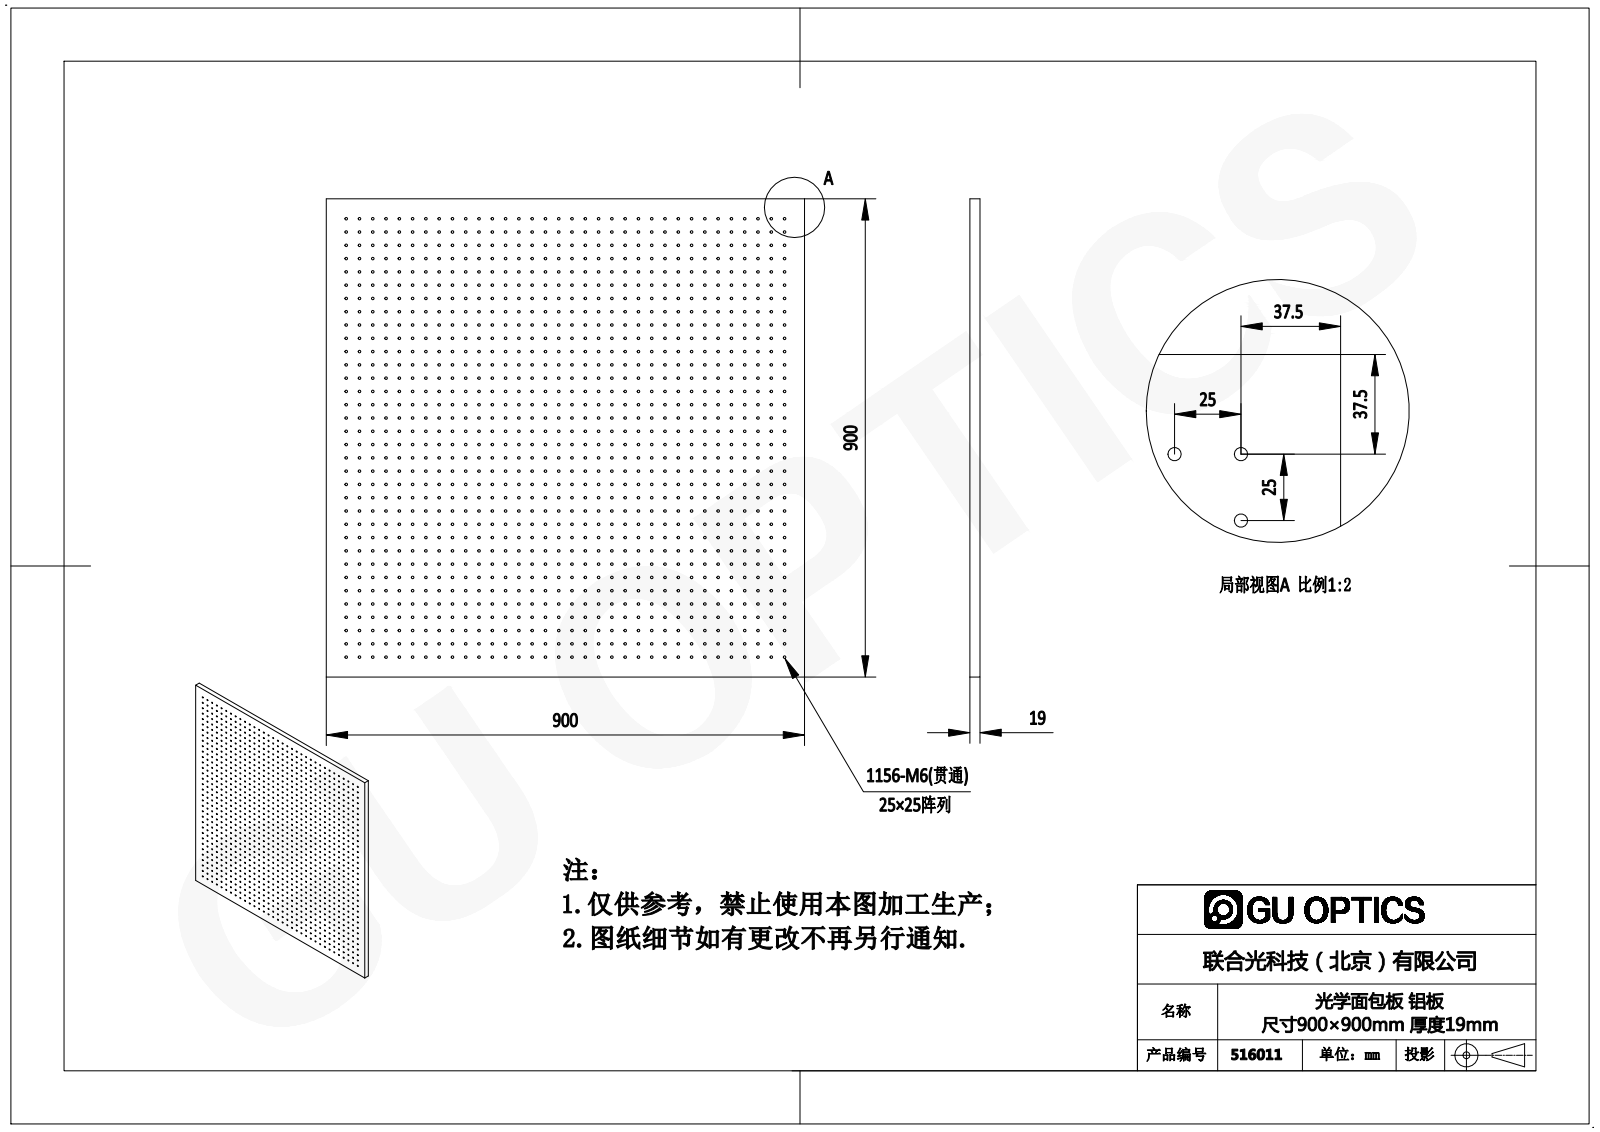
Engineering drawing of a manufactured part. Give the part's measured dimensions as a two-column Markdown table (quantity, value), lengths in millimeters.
| quantity | value |
| --- | --- |
| part name | 516011 |
| STEP written by | SolidWorks 2020 (CONFIG_CONTROL_DESIGN) |
| units | millimeters |
| bodies | 1 solid, 2456 faces (6 planar, 2450 cylindrical, 0 other) |
| overall size | 900 × 900 × 19 |
| volume | 14 930 000 mm³ |
| surface area | 2 006 000 mm² |
| round holes (diameter × count) | 5 × 1225 |
| main face-to-face distances | 19, 900 |
| hole center spacings | 25, 50, 75, 100, 125, 150, 175, 200 |
